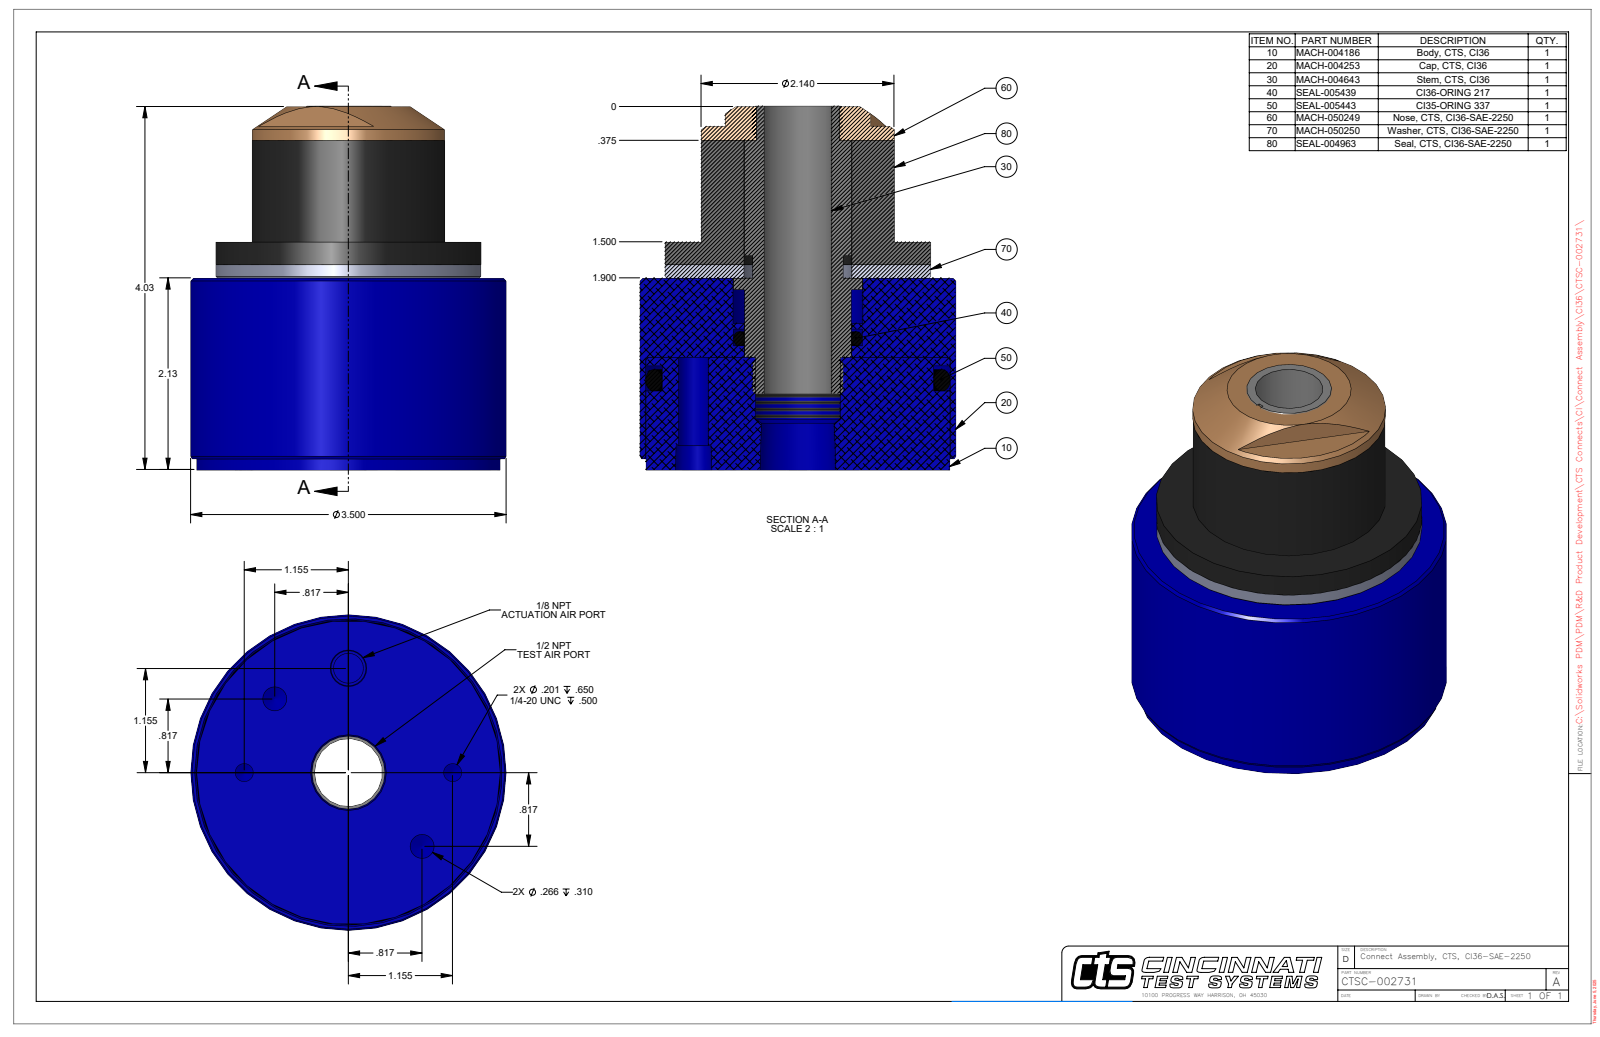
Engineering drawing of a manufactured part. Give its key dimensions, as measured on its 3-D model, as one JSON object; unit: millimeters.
{"part_name": "CTSC-002731", "step_written_by": "SolidWorks 2023 (AUTOMOTIVE_DESIGN)", "units": "millimeters", "bodies": {"solids": 2, "faces": 76, "planar": 20, "cylindrical": 29, "other": 27}, "overall_size": [102.4, 88.9, 88.9], "volume_mm3": 428200, "surface_area_mm2": 51820, "round_holes": [[5.1, 2], [6.8, 2], [8.4, 1], [19.1, 1], [23.8, 1], [36.5, 1], [85.7, 1]], "round_bosses_or_shafts": [[88.9, 1], [85.5, 1], [74.8, 1], [54.4, 1], [36.2, 1]], "partial_cylinders_radius": [[11.7, 1]], "face_to_face_distances": [64.1, 54, 10.2, 32.5, 42.7, 102.2, 48.3, 38.1, 96.7, 5.6], "hole_center_spacings": [22.5, 29.3, 54.2, 29.3, 41.5, 58.6, 58.7]}
